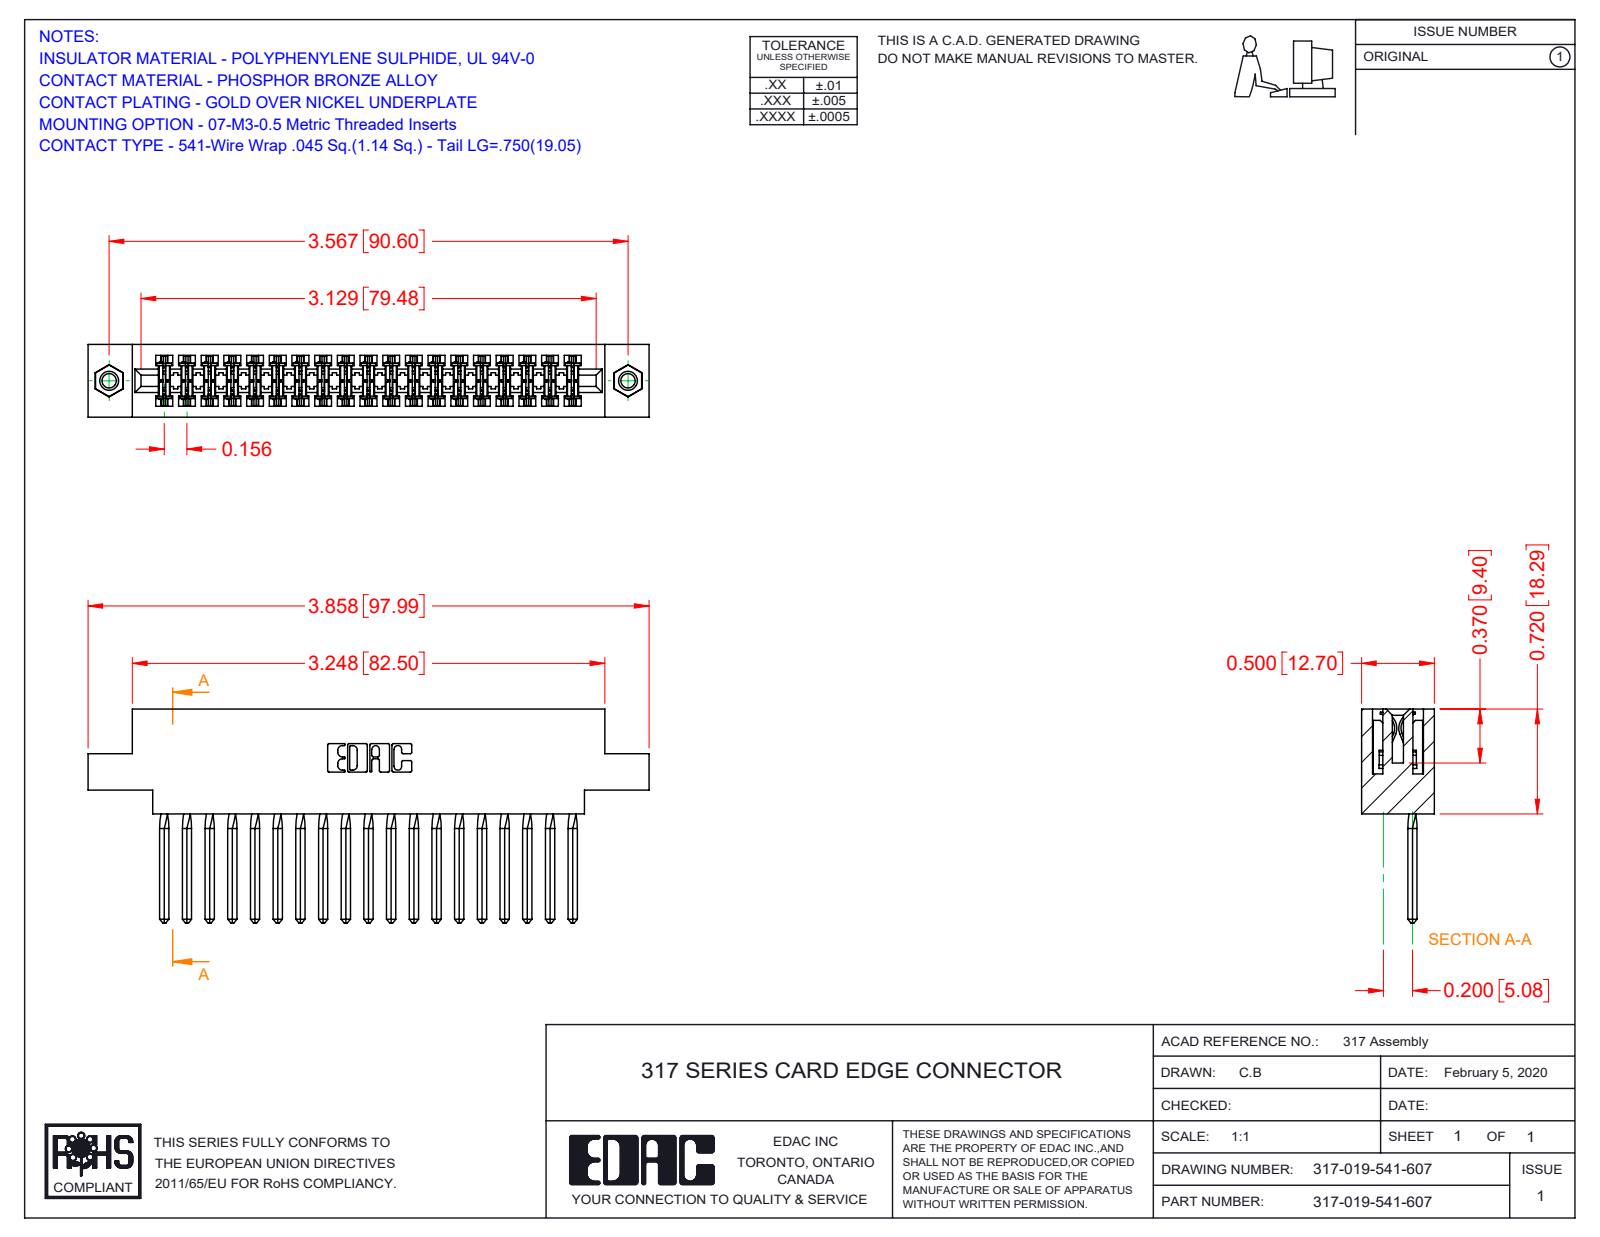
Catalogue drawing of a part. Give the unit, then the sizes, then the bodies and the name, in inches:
Units: inches
Overall size (bounding box): 3.858 × 1.47 × 0.5
Round holes (diameter × count): ⌀0.098 ×2, ⌀0.125 ×2, ⌀0.156 ×2
Round bosses / shafts (diameter × count): ⌀0.155 ×2
Partial cylindrical surfaces — rounded edges, fillets, slot ends (radius × count): R0.015 ×38, R0.01 ×22, R0.007 ×6, R0.031 ×6, R0.026 ×3, R0.095 ×2, R0.1 ×2, R0.11 ×2
Main face-to-face distances: 0.5, 0.075, 0.425, 0.11, 0.35, 0.195, 0.772, 0.22, 0.662, 0.72
Hole centre spacings: 3.567
Volume: 0.926 in³ · Surface area: 32.09 in²
Bodies: 22 solids, 3050 faces (2446 planar, 512 cylindrical, 92 other)
Part name (STEP PRODUCT): 317-019-541-607; 317 Part_.156 Dia - TI; 345-250-001_345-250-005-103; 317-290-002_541
STEP written by: SolidWorks 2016 (CONFIG_CONTROL_DESIGN)
